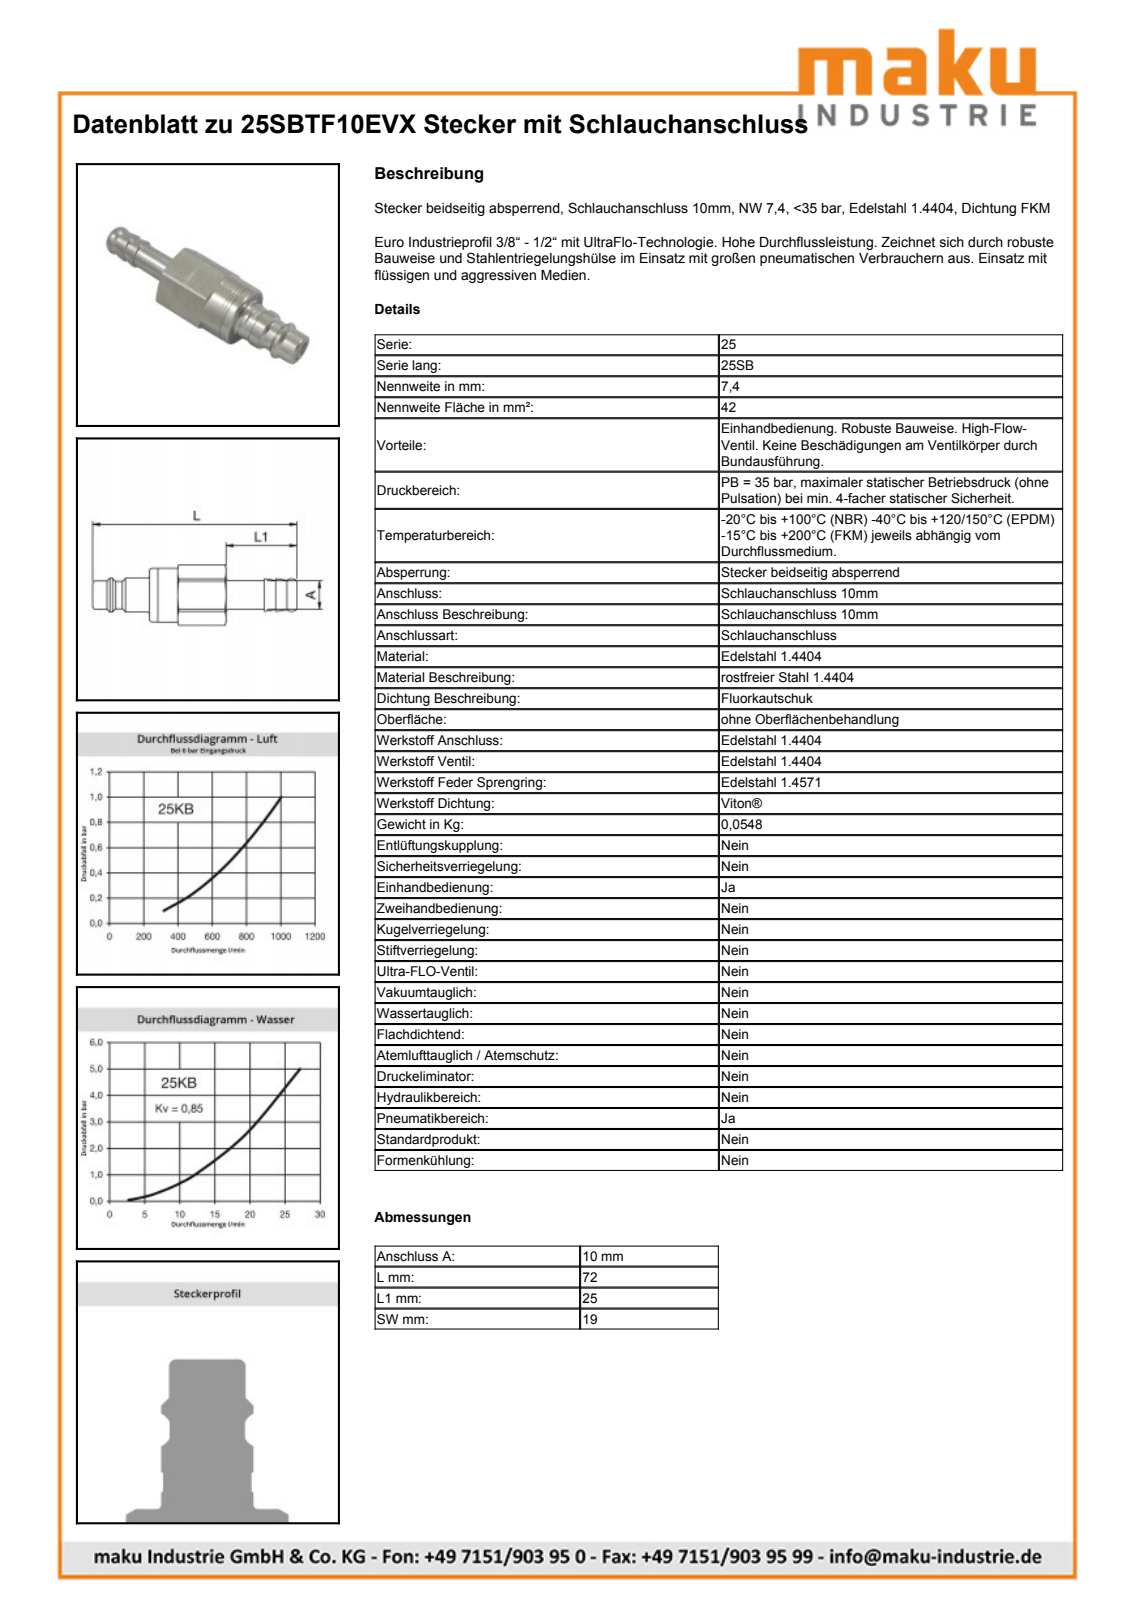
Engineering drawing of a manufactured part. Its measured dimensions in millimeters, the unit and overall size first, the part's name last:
Units: millimetres
Overall size (bounding box): 72 × 21.38 × 19.83
Round holes (diameter × count): ⌀16 ×1
Round bosses / shafts (diameter × count): ⌀19 ×1, ⌀18.95 ×1, ⌀15.27 ×1, ⌀12 ×1, ⌀10.1 ×1, ⌀9.9 ×1, ⌀9.75 ×1
Partial cylindrical surfaces — rounded edges, fillets, slot ends (radius × count): R10.7 ×1
Main face-to-face distances: 19, 27, 52, 25, 20, 47, 72, 3, 4.5, 27.5
Volume: 12 113 mm³ · Surface area: 4 303 mm²
Bodies: 1 solid, 55 faces (15 planar, 17 cylindrical, 23 other)
Part name (STEP PRODUCT): D105163
STEP written by: Autodesk Inventor 2011 (AUTOMOTIVE_DESIGN)
